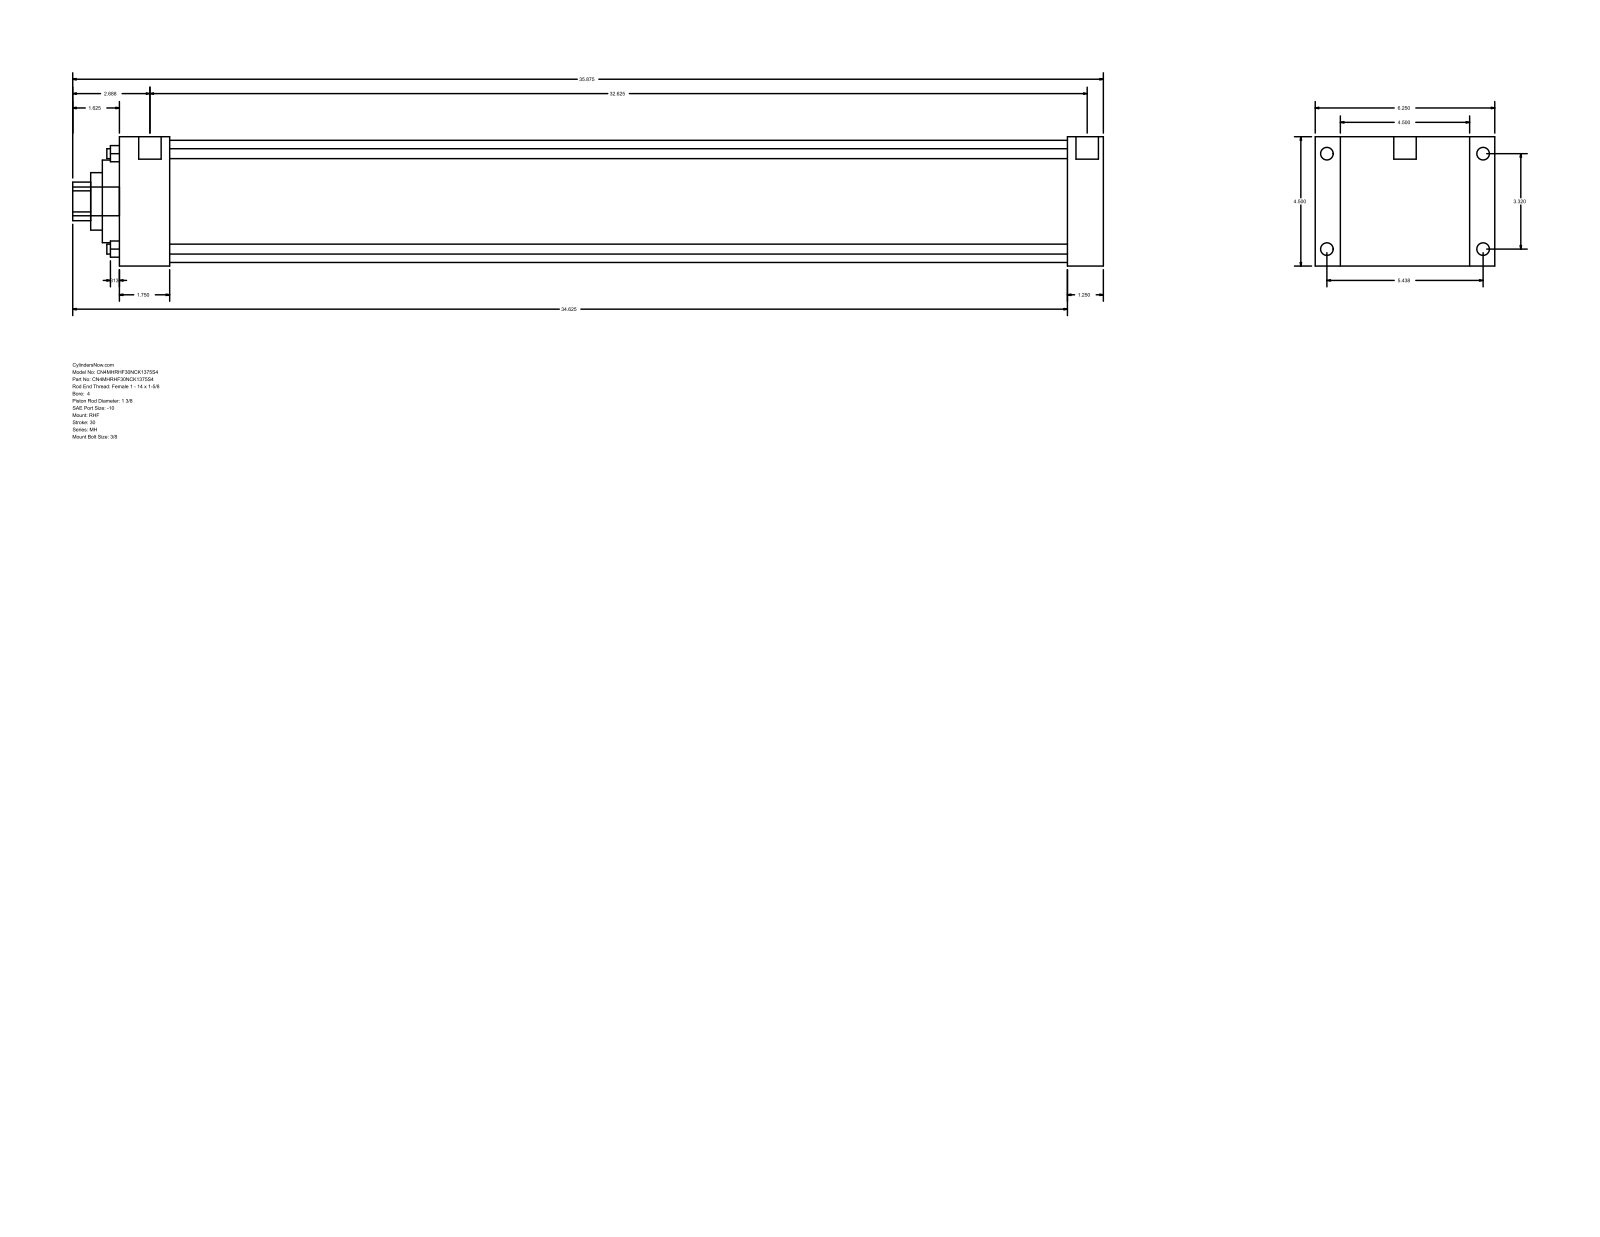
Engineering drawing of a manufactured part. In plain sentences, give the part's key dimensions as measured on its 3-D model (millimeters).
The part is named "MH_RHF__0400_1.375". Its 3-D file was written by "GSSL Pune (CONFIG_CONTROL_DESIGN)". It is 0 solids with 90 faces: 61 planar, 29 cylindrical and 0 other. Overall it measures 911.23 by 158.75 by 114.3 millimeters. Round holes: 4 of diameter 8.76, 1 of diameter 34.92, 1 of diameter 50.8, 1 of diameter 73.03, 1 of diameter 107.95. Round bosses or shafts: 4 of diameter 11.13, 4 of diameter 8.73, 2 of diameter 19.84, 1 of diameter 25.4. Partial cylindrical surfaces (rounded edges, fillets, slot ends): 1 of radius 17.06. The main face-to-face distances are 114.3, 869.96, 838.21, 31.75, 22.23, 136.53, 44.45, 793.76, 825.51, 158.76. The hole center spacings are 59.62, 84.32, 119.25.
